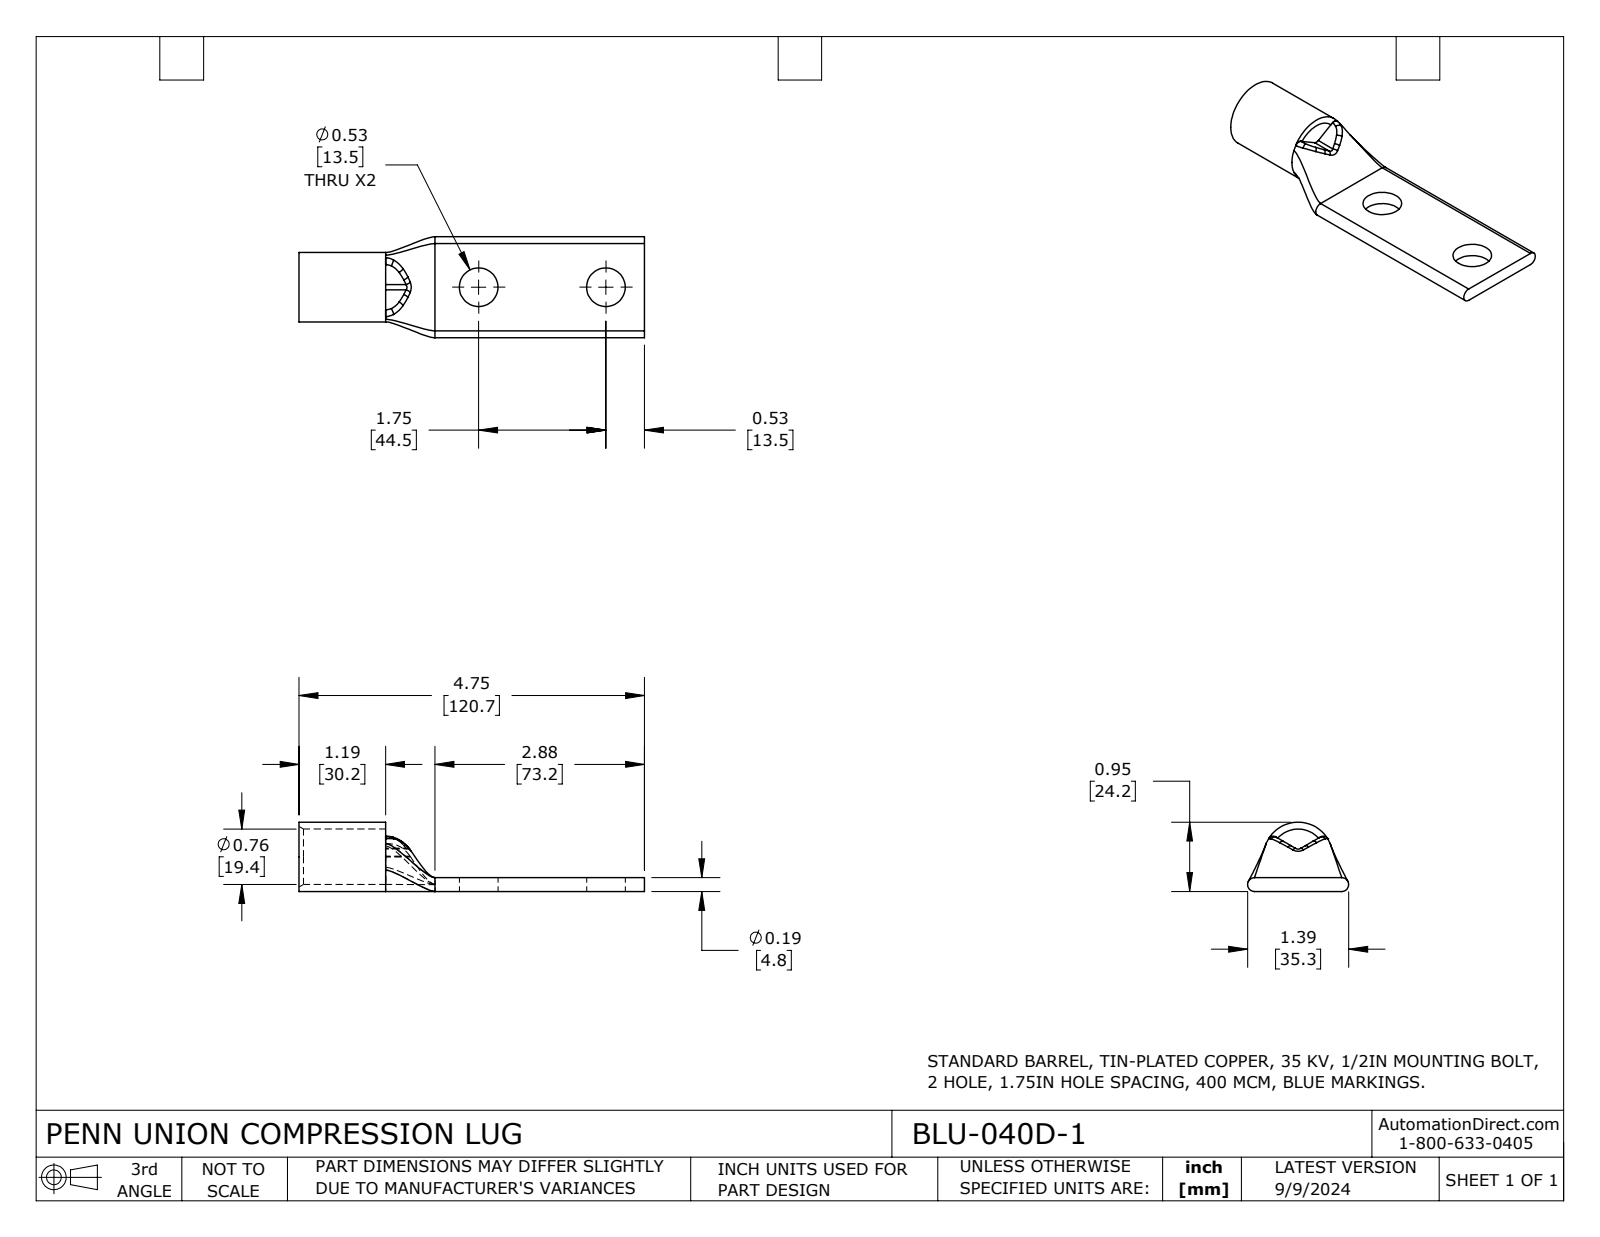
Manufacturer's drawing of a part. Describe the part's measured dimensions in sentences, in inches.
The part is named "BLU-040D-1". Its 3-D file was written by "SolidWorks 2023 (CONFIG_CONTROL_DESIGN)". It is 1 solid with 45 faces: 11 planar, 13 cylindrical and 21 other. Overall it measures 4.75 by 1.39 by 0.953 inches. Its volume is 1.121 cubic inches and its surface area 19.44 square inches. Round holes: 2 of diameter 0.531, 1 of diameter 0.762. Round bosses or shafts: 1 of diameter 0.953. Partial cylindrical surfaces (rounded edges, fillets, slot ends): 2 of radius 0.07, 2 of radius 0.095. The main face-to-face distances are 0.19, 4.75, 1.19, 3.56, 0.095, 1.87, 0.68, 2.88. The hole center spacings are 1.75.
